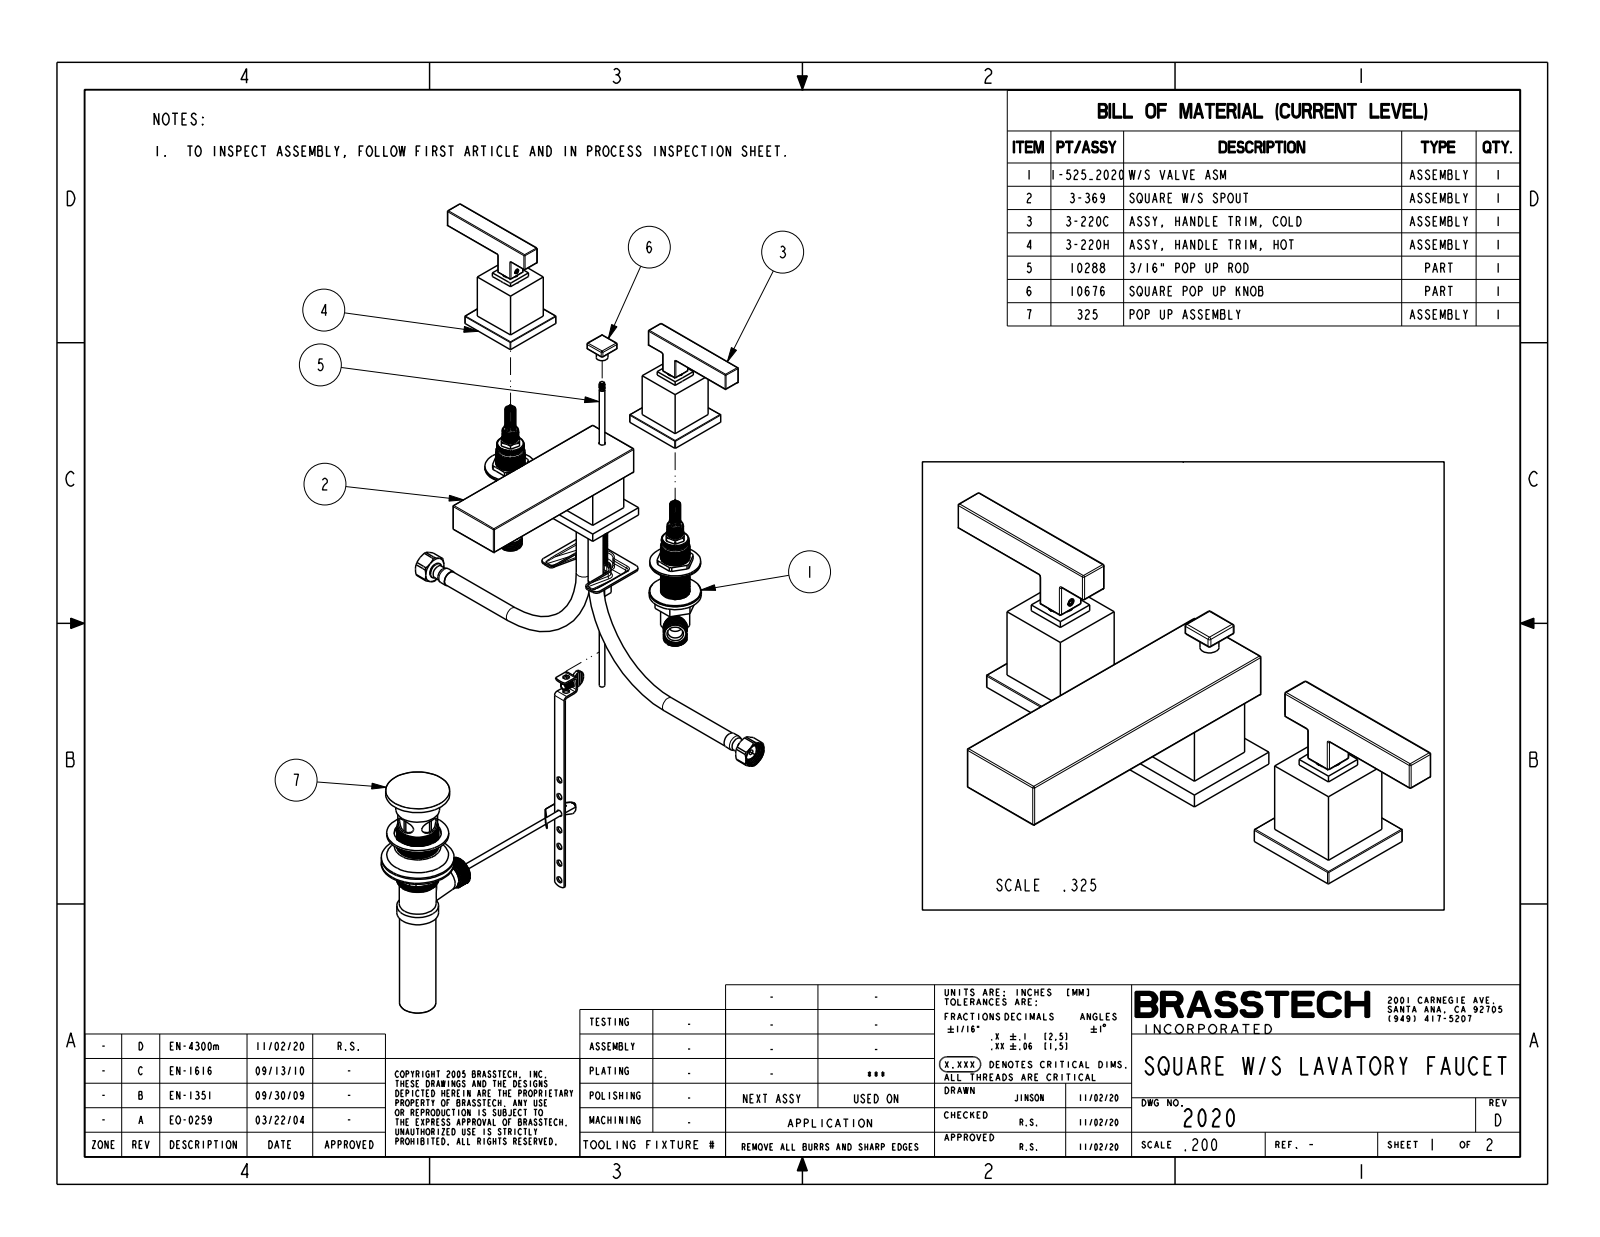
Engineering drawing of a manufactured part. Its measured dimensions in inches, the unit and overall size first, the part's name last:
Units: inches
Overall size (bounding box): 13.52 × 6.911 × 3.515
Round holes (diameter × count): ⌀0.792 ×1, ⌀1.29 ×1, ⌀1.92 ×1
Round bosses / shafts (diameter × count): ⌀0.4 ×3, ⌀0.8 ×2, ⌀0.925 ×1
Partial cylindrical surfaces — rounded edges, fillets, slot ends (radius × count): R0.03 ×50, R0.02 ×14, R0.04 ×12, R0.25 ×12, R0.697 ×1, R0.716 ×1, R0.726 ×1
Main face-to-face distances: 0.31, 2.798, 1.798, 1, 0.487, 1.113, 1.6, 8, 1.488, 2.488
Hole centre spacings: 4.968
Volume: 31.11 in³ · Surface area: 151.9 in²
Bodies: 3 solids, 277 faces (91 planar, 124 cylindrical, 62 other)
Part name (STEP PRODUCT): 2020
STEP written by: CREO PARAMETRIC BY PTC INC, 2018400 (CONFIG_CONTROL_DESIGN)
